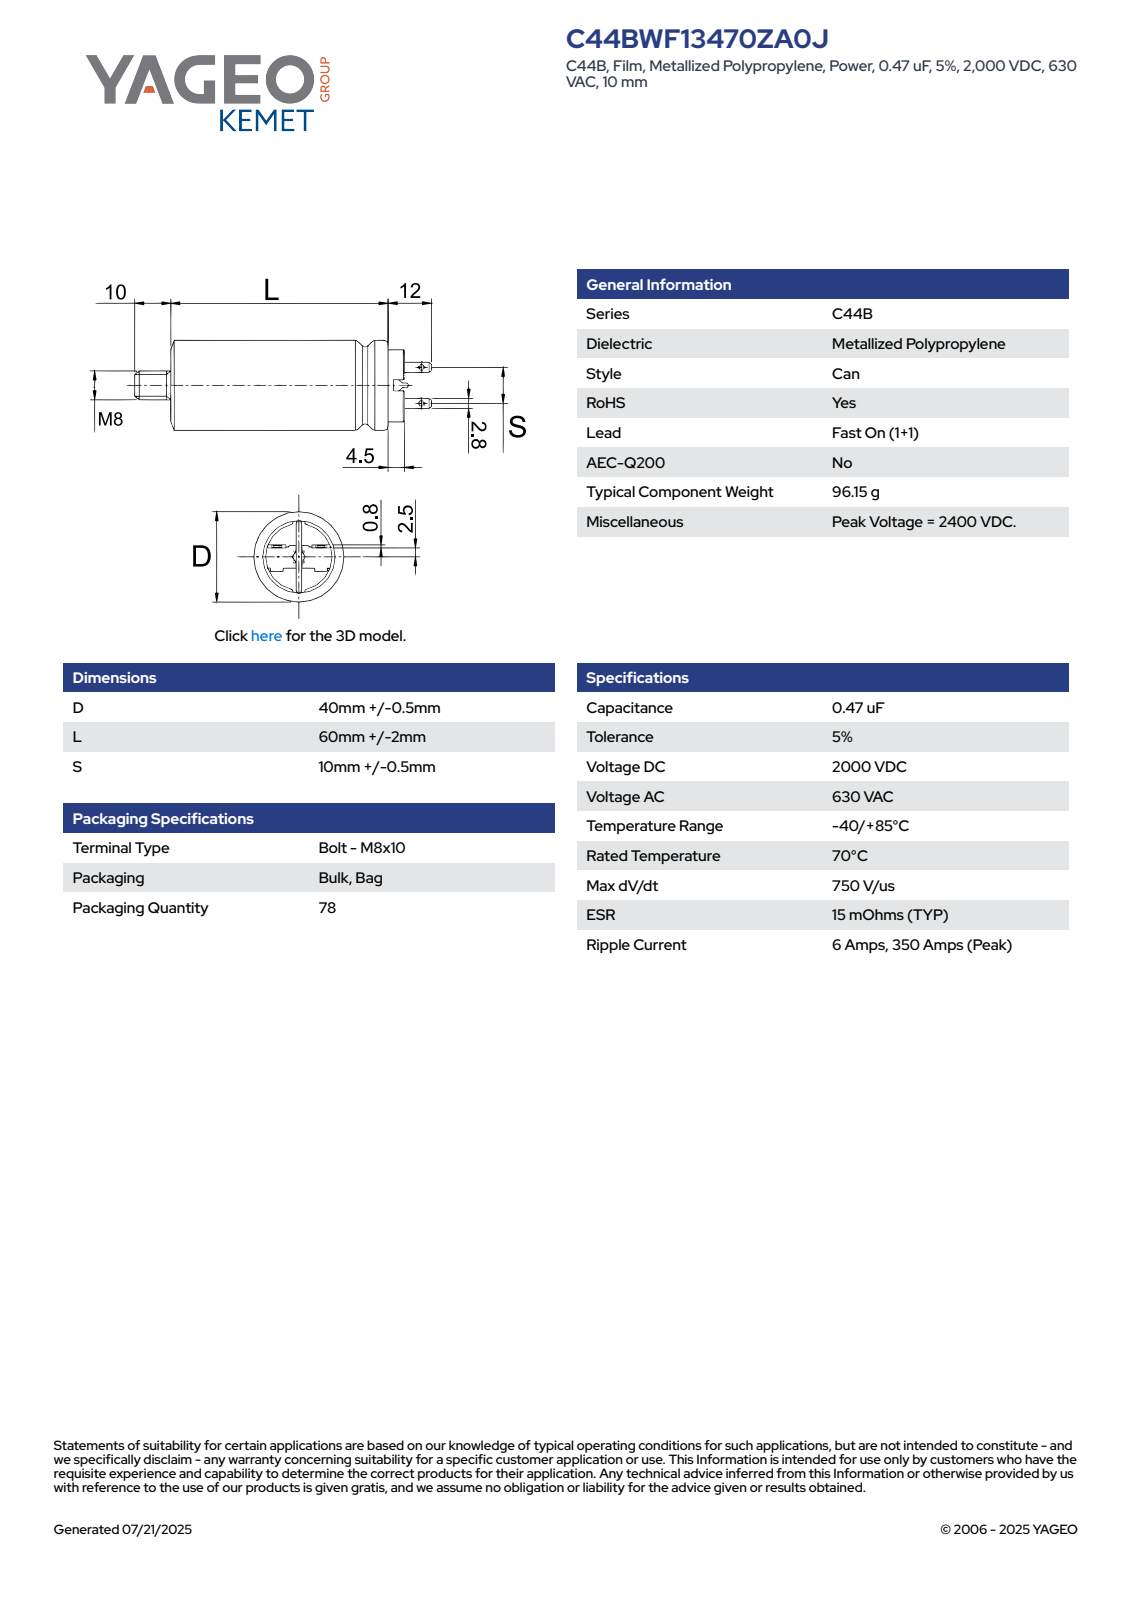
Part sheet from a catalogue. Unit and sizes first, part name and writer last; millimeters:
Units: millimetres
Overall size (bounding box): 84 × 40.5 × 40.5
Round bosses / shafts (diameter × count): ⌀40.5 ×1, ⌀32.04 ×1, ⌀30.04 ×1, ⌀8 ×1
Partial cylindrical surfaces — rounded edges, fillets, slot ends (radius × count): R0.2 ×6, R0.68 ×1, R20.24 ×1
Main face-to-face distances: 62, 66.5, 4.5, 0.8, 10, 72, 76.5, 2.8, 10.5, 2.25
Volume: 80 234 mm³ · Surface area: 12 031 mm²
Bodies: 1 solid, 132 faces (49 planar, 40 cylindrical, 43 other)
Part name (STEP PRODUCT): CFP_C44B_40X60_D40.5L62S10.5
STEP written by: SolidWorks 2014 (AUTOMOTIVE_DESIGN)
